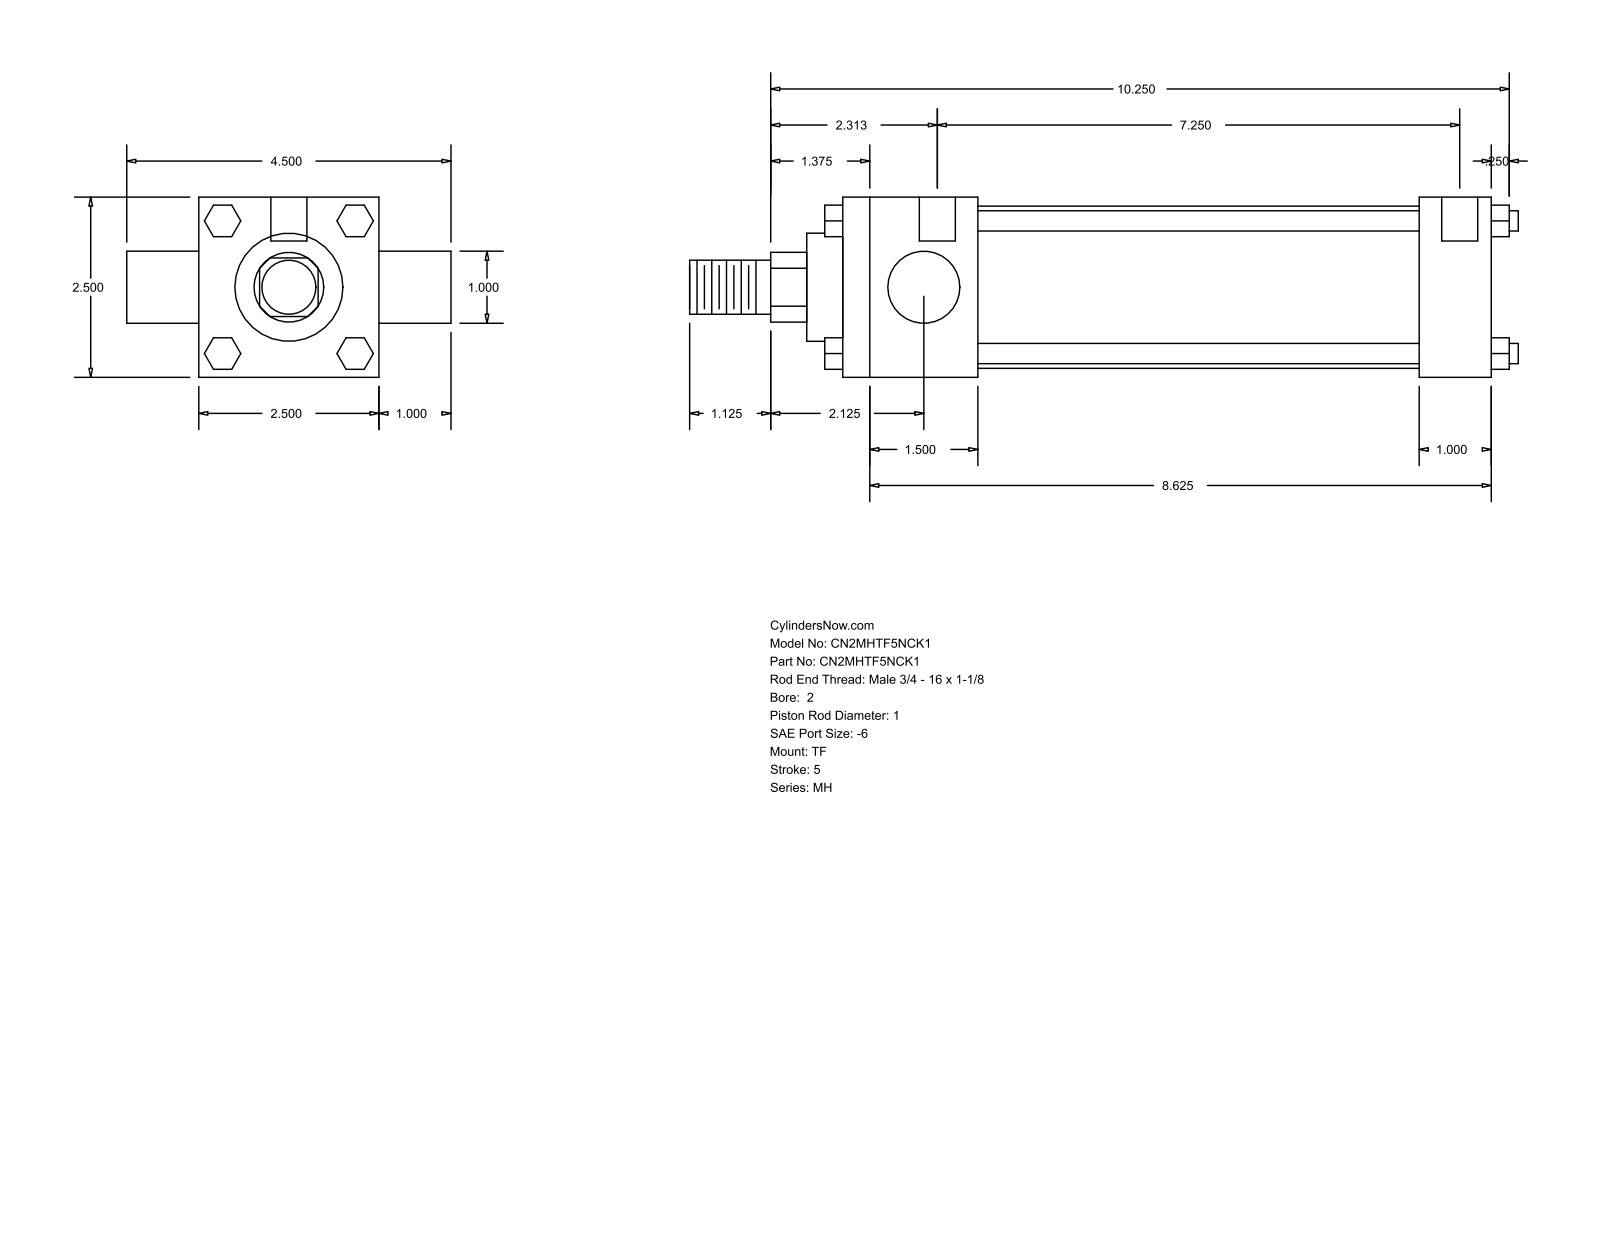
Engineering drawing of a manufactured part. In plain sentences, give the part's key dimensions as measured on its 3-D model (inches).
The part is named "MH_TF__0200_1". Its 3-D file was written by "GSSL Pune (CONFIG_CONTROL_DESIGN)". It is 0 solids with 120 faces: 92 planar, 28 cylindrical and 0 other. Overall it measures 11.5 by 4.5 by 2.5 inches. Round holes: 3 of diameter 0.219, 2 of diameter 0.5. Round bosses or shafts: 4 of diameter 0.281, 2 of diameter 1, 1 of diameter 2.25, 1 of diameter 1.5, 1 of diameter 0.75. Partial cylindrical surfaces (rounded edges, fillets, slot ends): 1 of radius 0.484. The main face-to-face distances are 2.5, 9, 1, 1.875, 8, 6.125, 7.125, 3.5, 9.5, 0.25. The hole center spacings are 0.125, 0.187, 7.25, 7.375, 7.437, 7.562.
